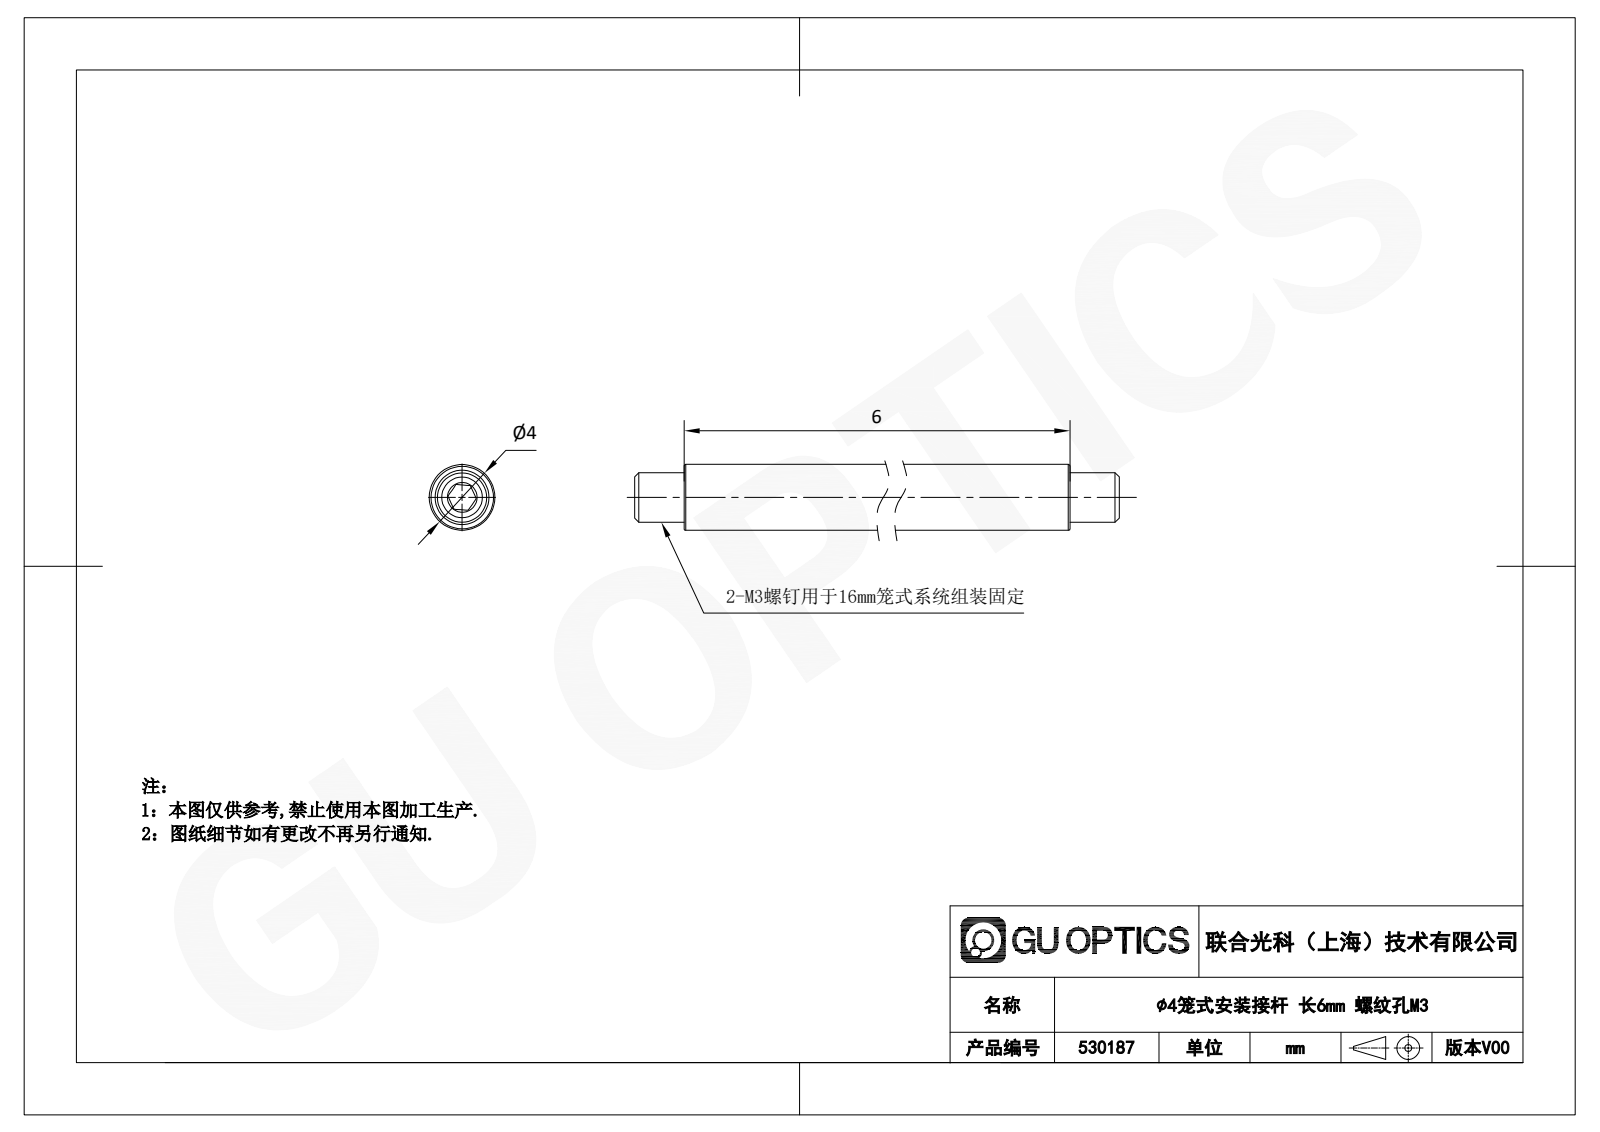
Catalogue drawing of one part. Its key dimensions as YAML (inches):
part_name: "530187"
step_written_by: "SolidWorks 2020 (CONFIG_CONTROL_DESIGN)"
units: inches
bodies: {solids: 3, faces: 34, planar: 20, cylindrical: 4, other: 10}
overall_size: [0.63, 0.157, 0.157]
volume: 0.009
surface_area: 0.487
round_holes:
  - {diameter: 0.098, count: 1}
round_bosses_or_shafts:
  - {diameter: 0.157, count: 1}
  - {diameter: 0.118, count: 1}
face_to_face_distances: [0.118, 0.197, 0.315, 0.433, 0.059, 0.236, 0.039, 0.591, 0.157, 0.276]
